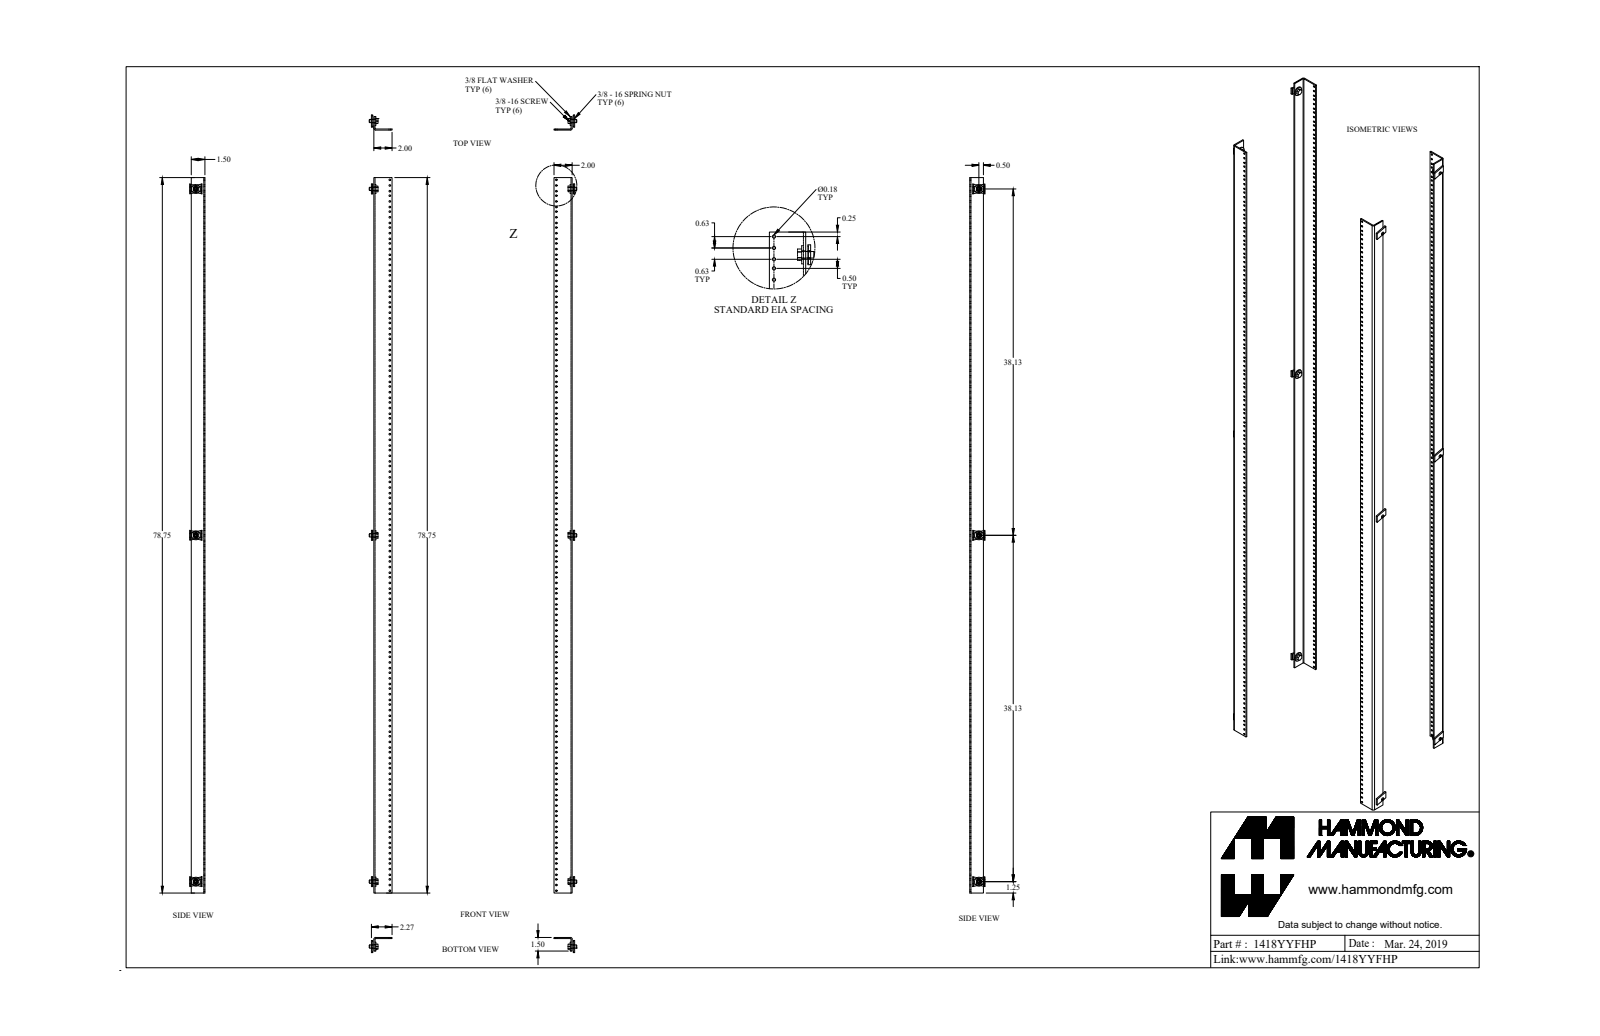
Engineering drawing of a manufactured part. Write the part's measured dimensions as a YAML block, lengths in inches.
part_name: "1418YYFHP_Default"
step_written_by: "SolidWorks 2019 (CONFIG_CONTROL_DESIGN)"
units: inches
bodies: {solids: 20, faces: 794, planar: 178, cylindrical: 604, other: 12}
overall_size: [78.75, 22.856, 1.668]
volume: 66.46
surface_area: 1129
round_holes:
  - {diameter: 0.177, count: 270}
  - {diameter: 0.313, count: 3}
  - {diameter: 0.437, count: 3}
  - {diameter: 0.445, count: 3}
round_bosses_or_shafts:
  - {diameter: 1, count: 3}
  - {diameter: 0.36, count: 3}
partial_cylinders:
  - {radius: 0.06, count: 2}
  - {radius: 0.185, count: 2}
face_to_face_distances: [0.125, 0.125, 21.84, 21.59, 21.715, 21.715, 1.5, 1.375, 1.375, 2]
hole_center_spacings: [1.75, 5.25, 3.5, 8.75, 7, 0.625, 0.625, 1.125]
